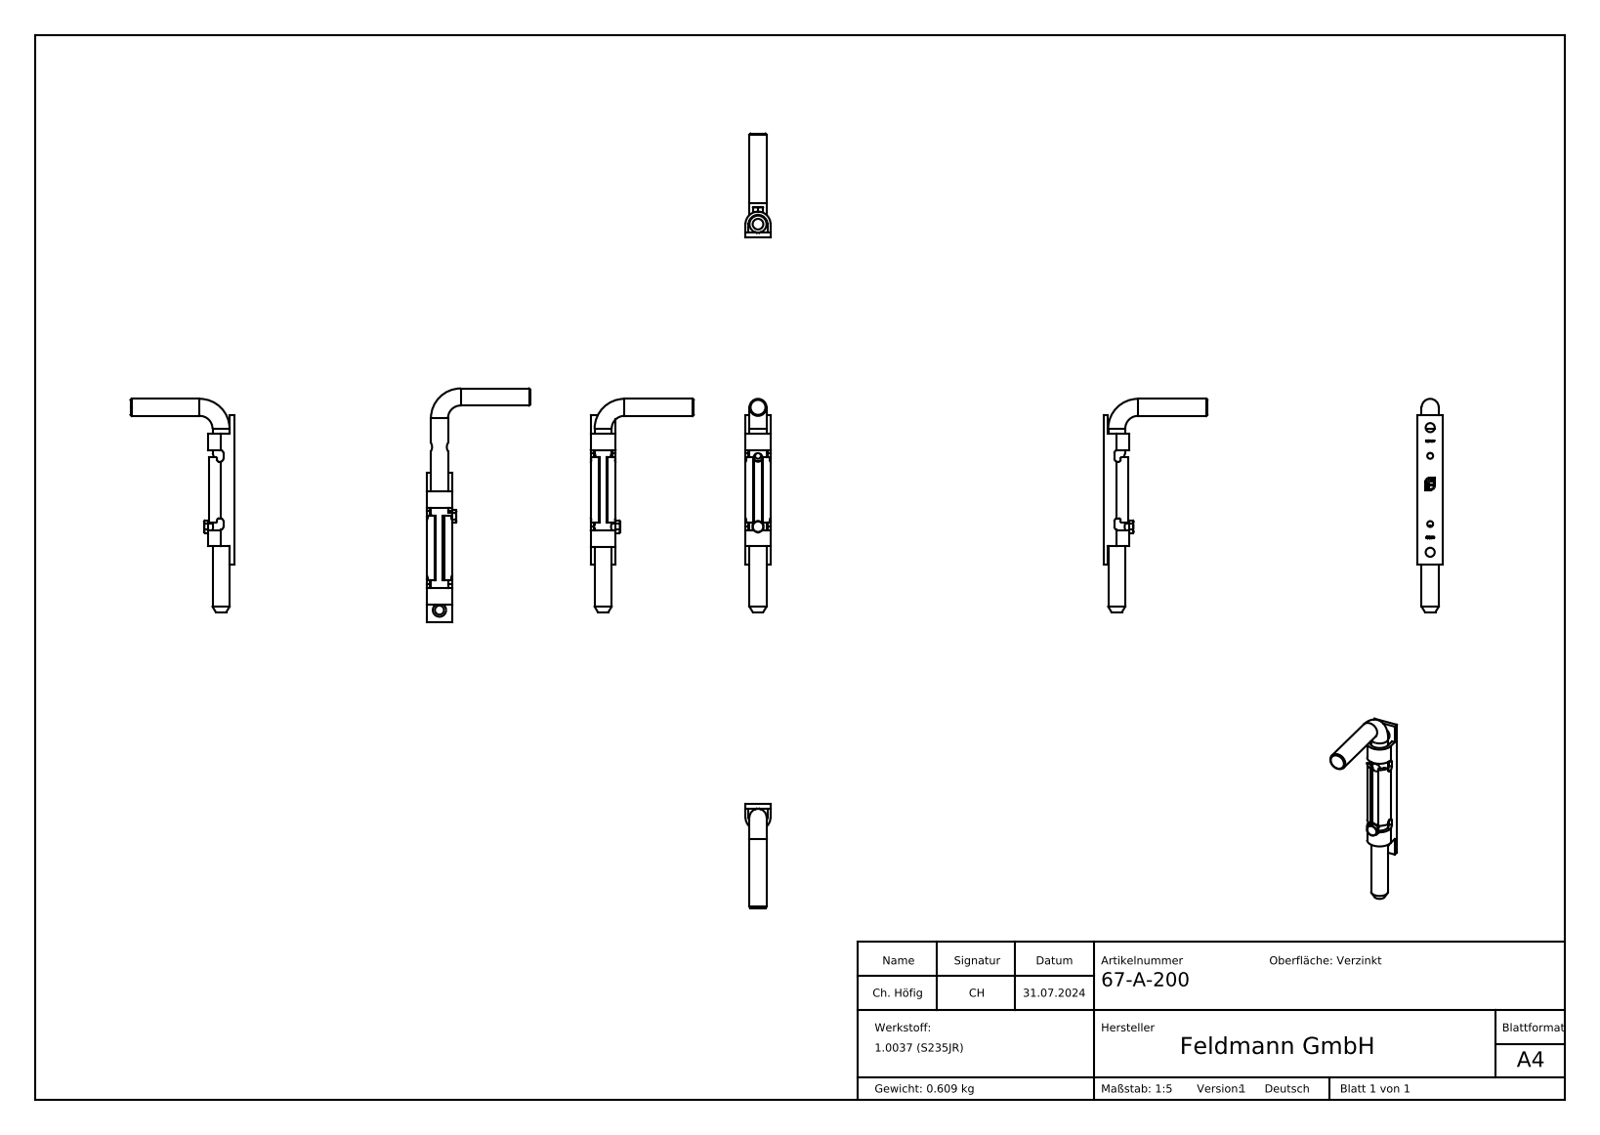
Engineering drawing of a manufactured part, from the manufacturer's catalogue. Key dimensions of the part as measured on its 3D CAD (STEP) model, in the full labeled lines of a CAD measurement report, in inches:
Part name (STEP PRODUCT): 67-A-X00 Teil1_67-A-200 Teil1; 67-A-200; 67-A-X00 Teil2_67-A-200 Teil2; DIN 931_DIN 931 M6x20
STEP written by: SolidWorks 2018 (CONFIG_CONTROL_DESIGN)
Units: inches
Bodies: 3 solids, 325 faces (175 planar, 33 cylindrical, 117 other)
Overall size (bounding box): 7.874 × 3.829 × 0.925
Volume: 4.764 in³ · Surface area: 48.71 in²
Round holes (diameter × count): ⌀0.217 ×2, ⌀0.335 ×2, ⌀0.197 ×1, ⌀0.315 ×1
Round bosses / shafts (diameter × count): ⌀0.63 ×2, ⌀0.236 ×1
Partial cylindrical surfaces — rounded edges, fillets, slot ends (radius × count): R0.118 ×4, R0.039 ×2, R0.079 ×2, R0.344 ×1, R0.463 ×1
Main face-to-face distances: 0.157, 0.118, 0.807, 0.925, 0.689, 0.669, 4.843, 1.28, 4.232, 0.61
Hole centre spacings: 1.043, 3.563, 0.059, 0.098, 0.945, 1.102, 2.461, 2.52
